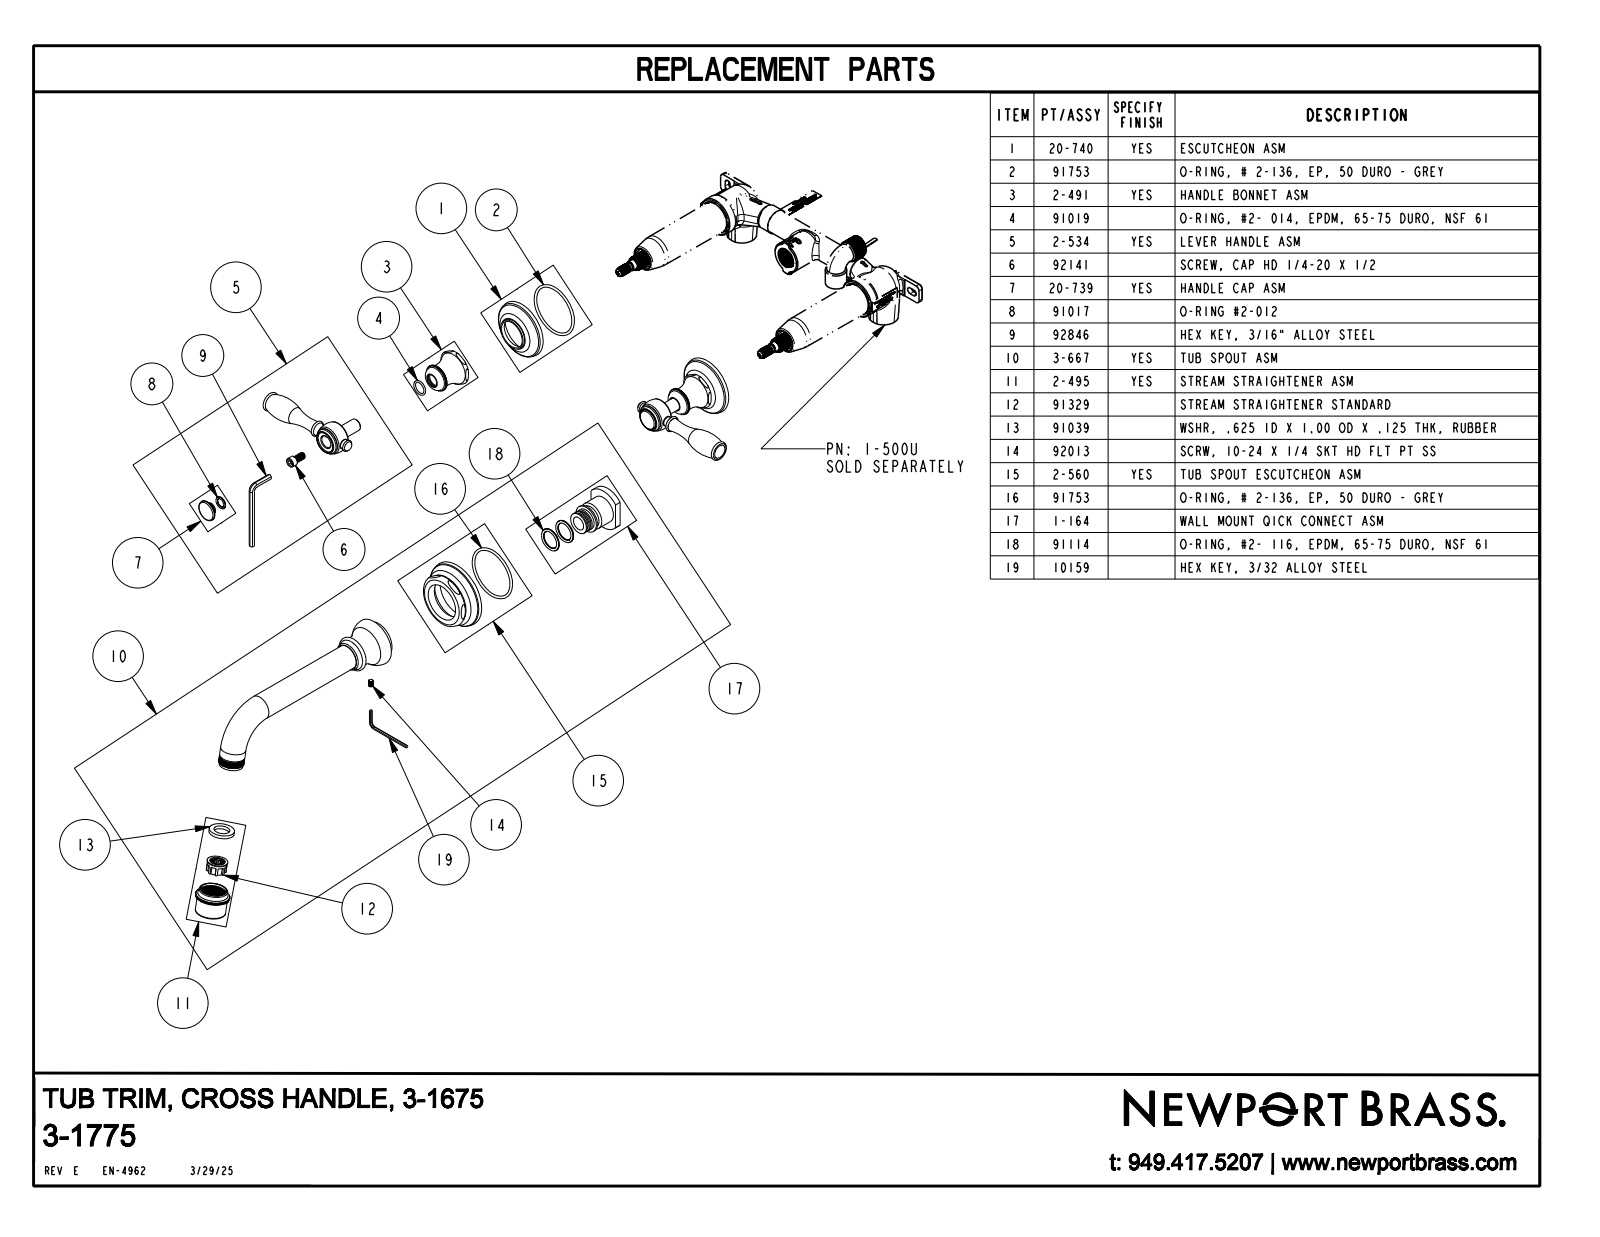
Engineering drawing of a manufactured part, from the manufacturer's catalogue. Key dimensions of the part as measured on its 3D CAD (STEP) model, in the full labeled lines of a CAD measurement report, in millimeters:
Part name (STEP PRODUCT): 3-1775_SW0001
STEP written by: CREO PARAMETRIC BY PTC INC, 2018400 (AUTOMOTIVE_DESIGN)
Units: millimetres
Bodies: 3 solids, 672 faces (494 planar, 34 cylindrical, 144 other)
Overall size (bounding box): 385.2 × 272.5 × 240.2
Volume: 370 700 mm³ · Surface area: 67 550 mm²
Round holes (diameter × count): ⌀21.7 ×2, ⌀10.4 ×1
Round bosses / shafts (diameter × count): ⌀25.4 ×2, ⌀21.3 ×2, ⌀12.7 ×2, ⌀30.5 ×1, ⌀10 ×1
Main face-to-face distances: 21.3, 85.9, 64.5, 53.3, 34.9, 34.9, 103.9, 82.6, 18, 105.2
Hole centre spacings: 200
